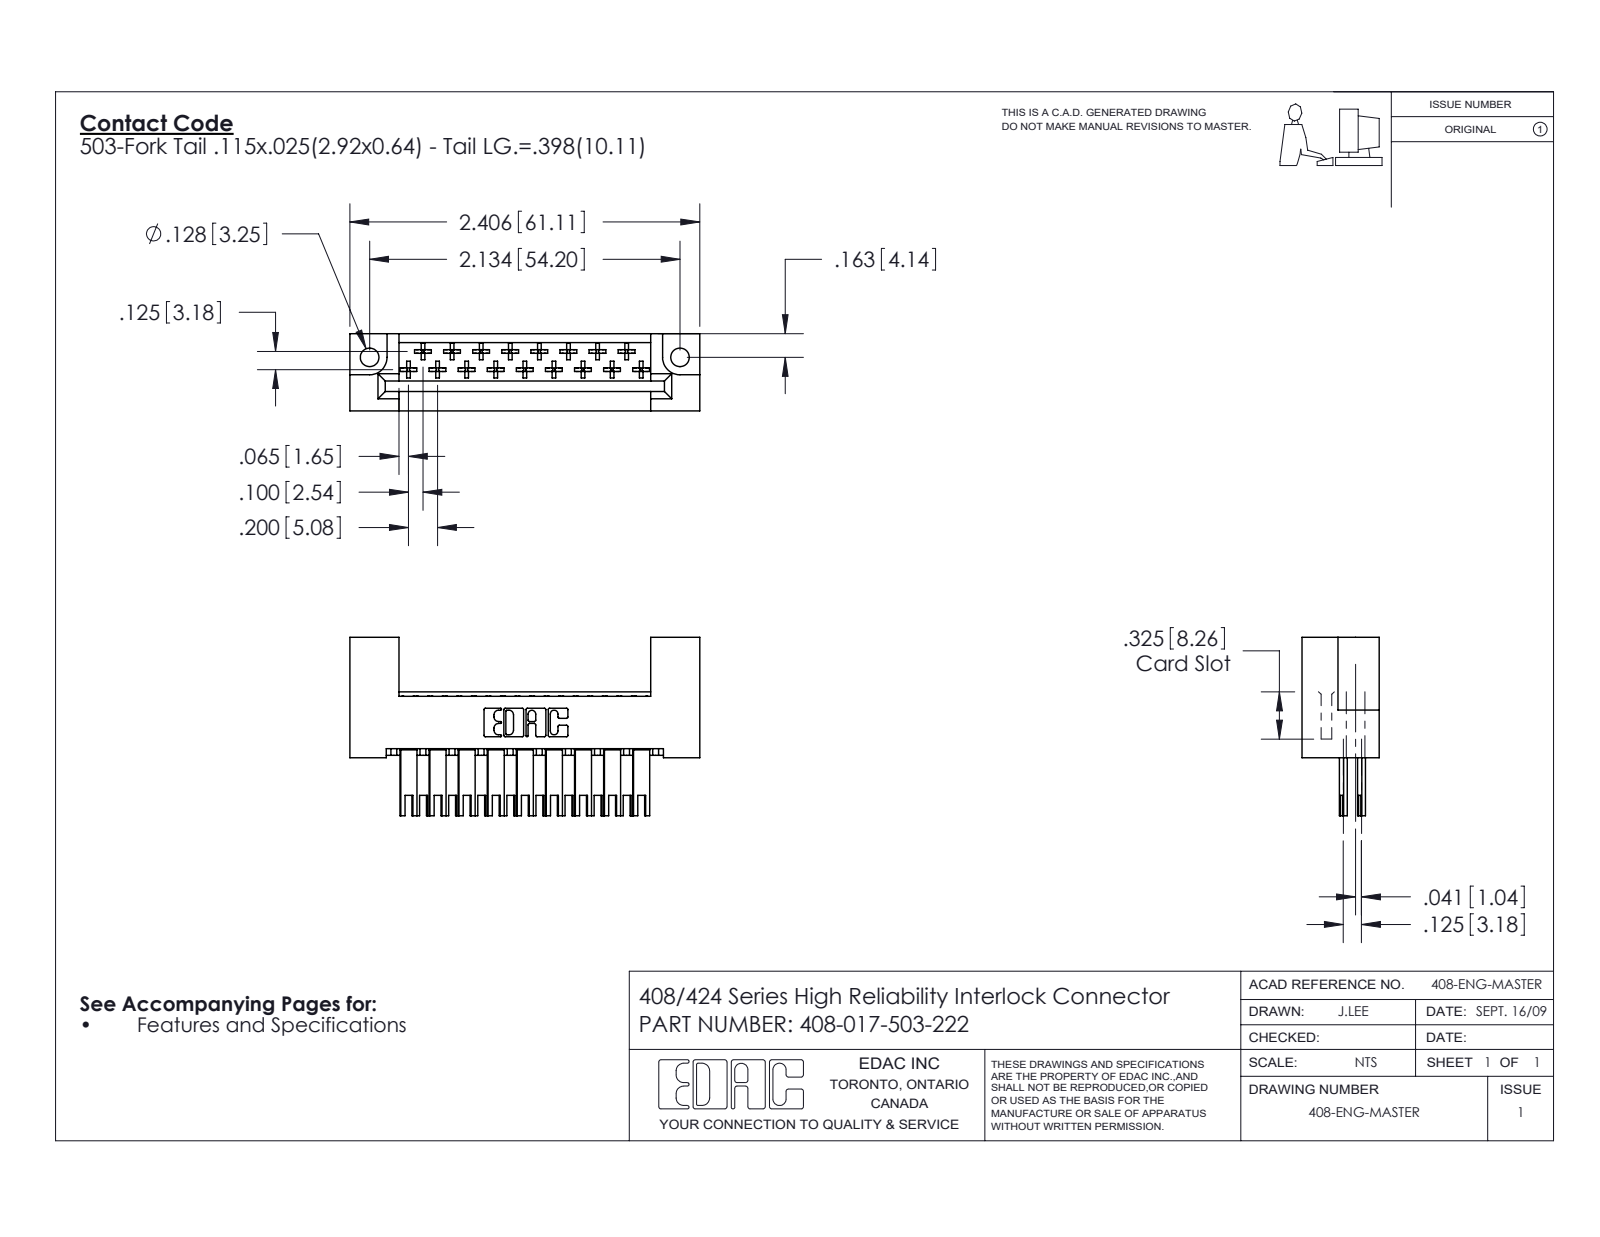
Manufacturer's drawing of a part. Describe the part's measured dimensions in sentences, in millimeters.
The part is named "408 Part_017 - 2; 408-290-001_408-290-103; 408-017-503-222". Its 3-D file was written by "SolidWorks 2016 (CONFIG_CONTROL_DESIGN)". It is 18 solids with 1040 faces: 786 planar, 186 cylindrical and 68 other. Overall it measures 61.1 by 31.1 by 13.5 millimeters. Its volume is 8 460 cubic millimeters and its surface area 9 626 square millimeters. Round holes: 2 of diameter 3.3. Partial cylindrical surfaces (rounded edges, fillets, slot ends): 102 of radius 0.3, 22 of radius 0.3, 19 of radius 0.5, 6 of radius 0.2, 6 of radius 0.8, 3 of radius 0.7, 2 of radius 3. The main face-to-face distances are 13.5, 0.6, 3.2, 0.6, 2.5, 10.1, 9.2, 8.3, 1.8, 5.2. The hole center spacings are 54.2.
